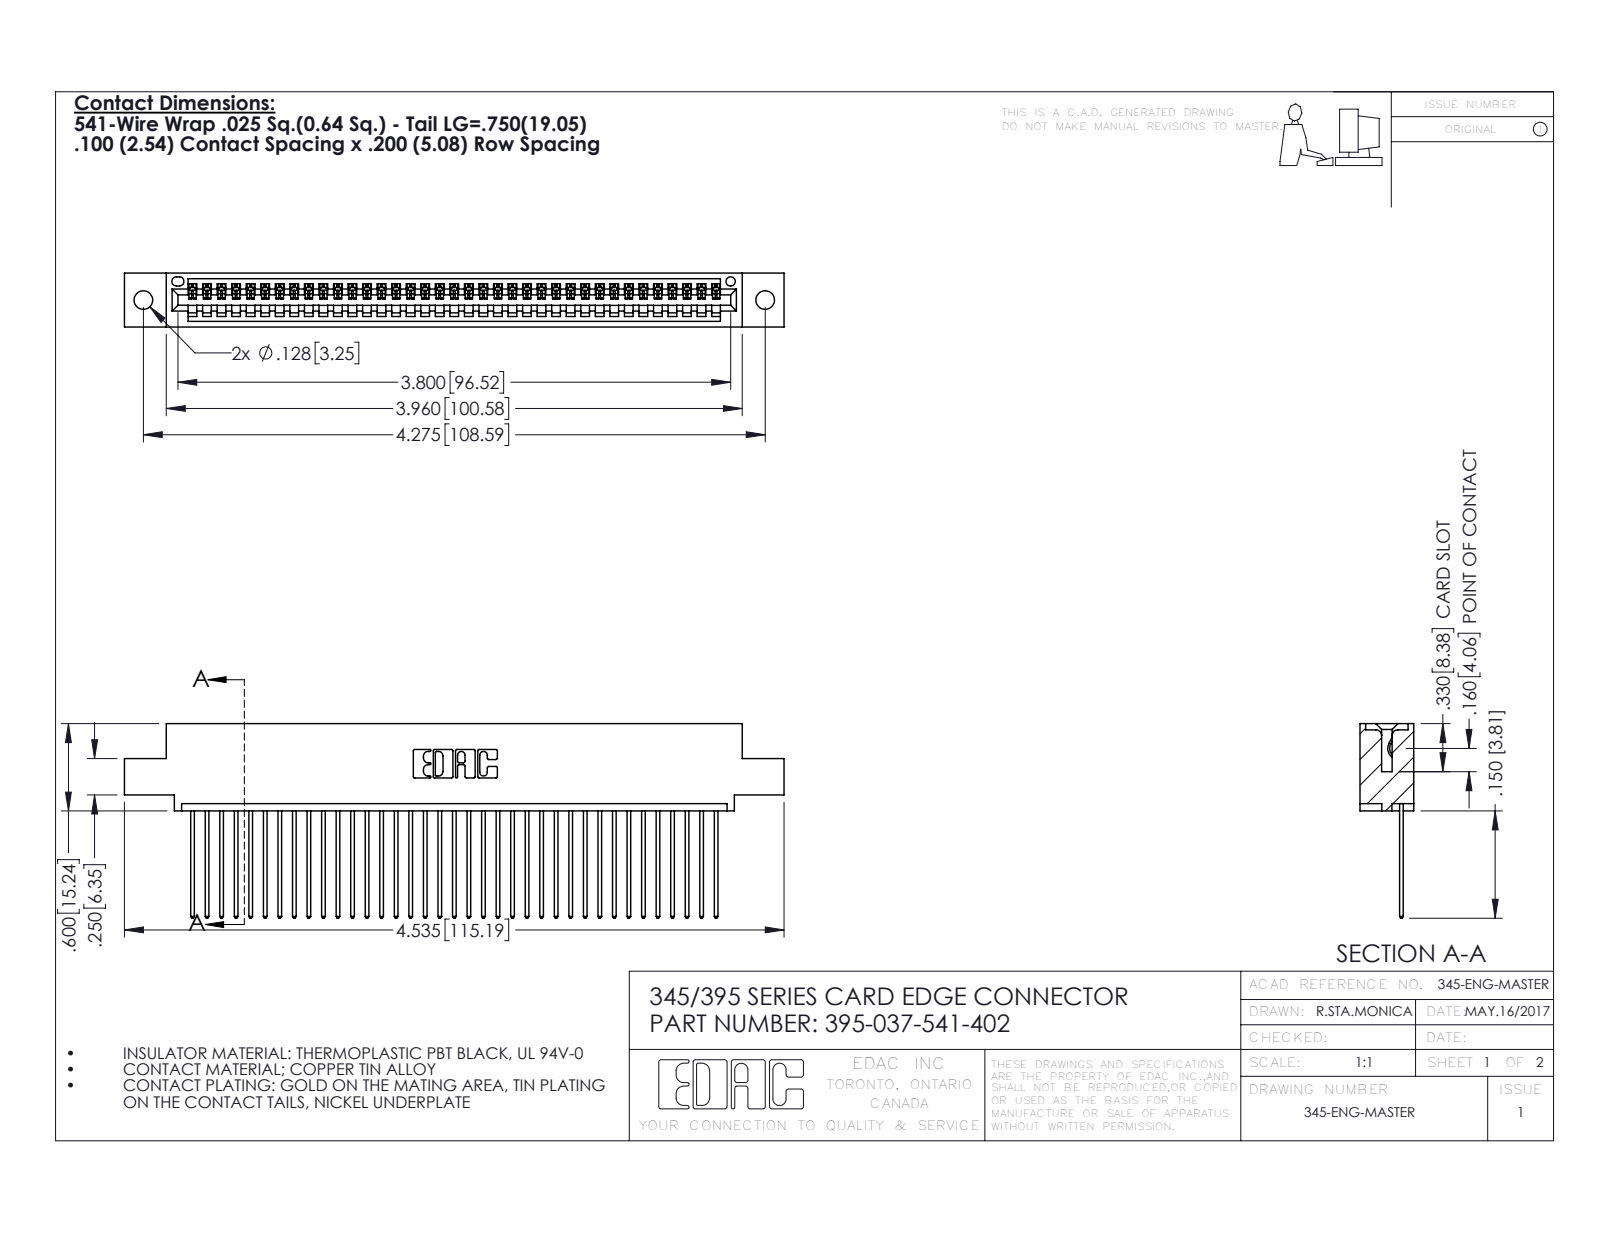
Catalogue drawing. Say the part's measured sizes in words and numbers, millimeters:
The part is named "345-292-001_345-293-141; 345 Part_0.110 Offset - 0.128 Dia; 395-037-541-402". Its 3-D file was written by "SolidWorks 2016 (CONFIG_CONTROL_DESIGN)". It is 38 solids with 2276 faces: 1564 planar, 712 cylindrical and 0 other. Overall it measures 115.2 by 34 by 9.4 millimeters. Its volume is 10 900 cubic millimeters and its surface area 14 960 square millimeters. Round holes: 2 of diameter 3.3, 1 of diameter 1.6. Partial cylindrical surfaces (rounded edges, fillets, slot ends): 74 of radius 0.2, 74 of radius 0.3, 22 of radius 0.3, 6 of radius 0.2, 6 of radius 0.8, 3 of radius 0.7, 2 of radius 0.8, 2 of radius 1. The main face-to-face distances are 1.8, 7.6, 2.5, 6.9, 0.6, 9.4, 5.1, 5.7, 3.8, 1.8. The hole center spacings are 6.9, 102.6, 108.6.
